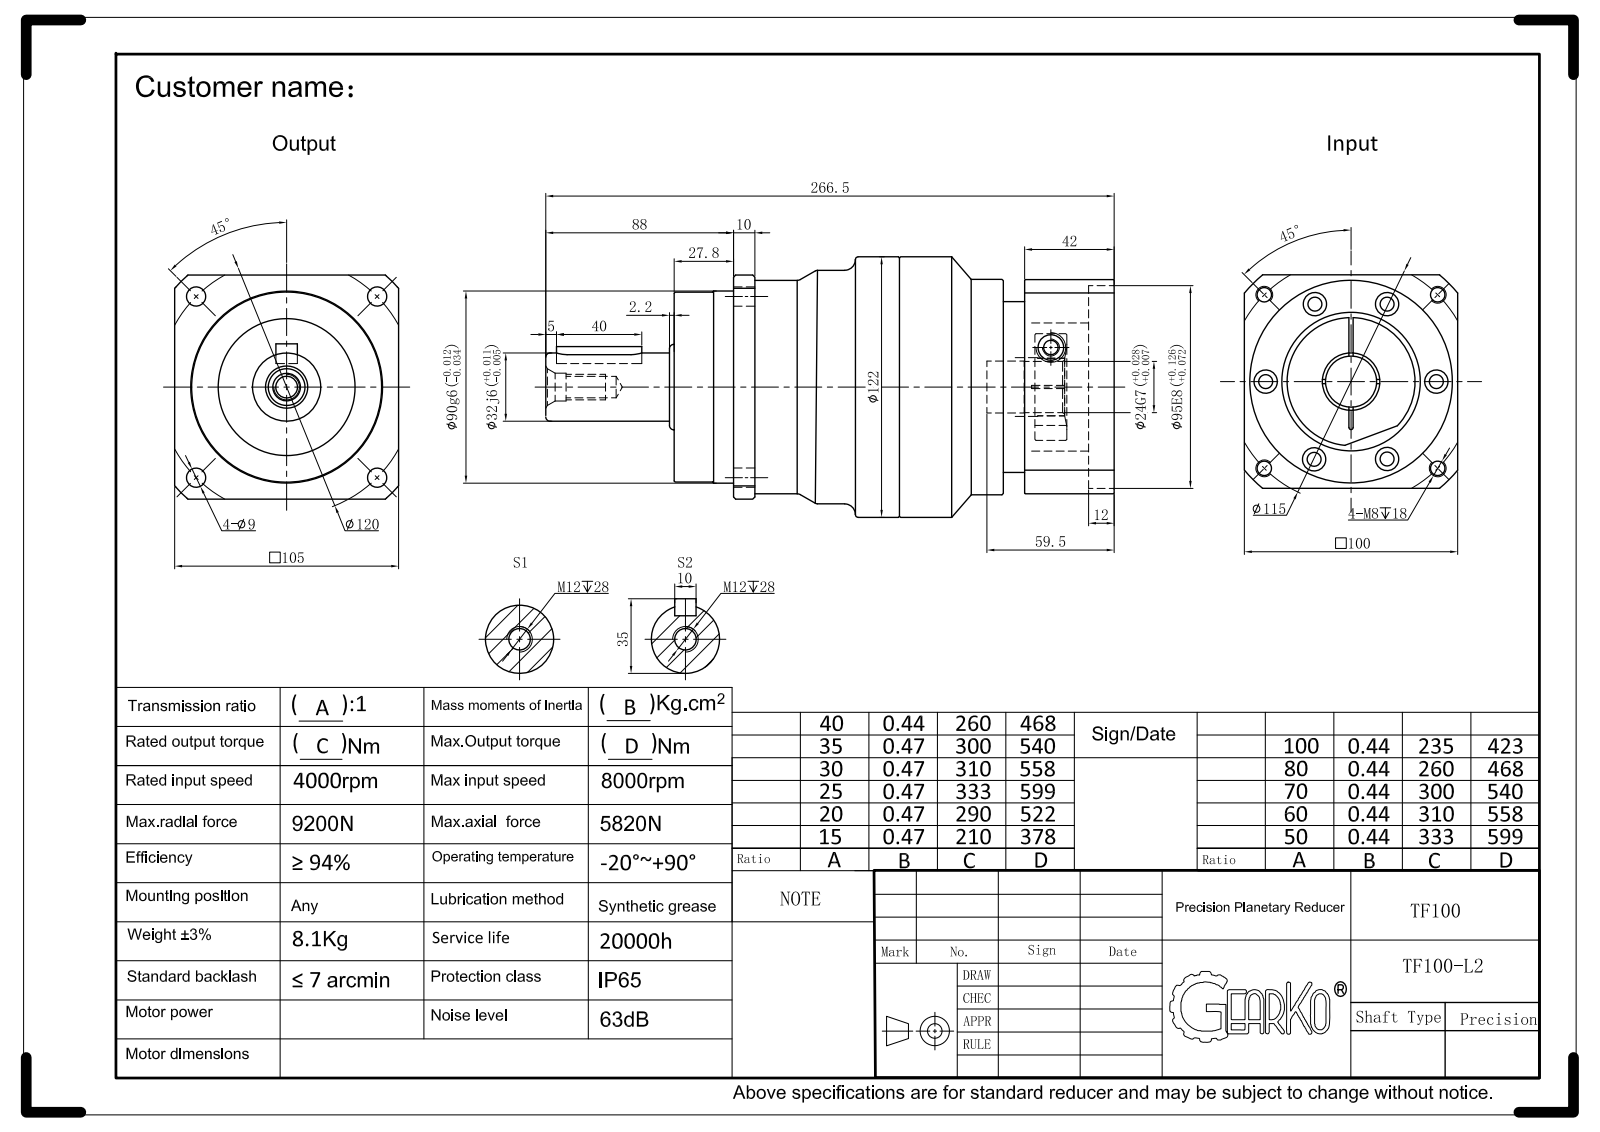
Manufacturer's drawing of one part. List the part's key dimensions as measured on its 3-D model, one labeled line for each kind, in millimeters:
STEP written by: SolidWorks 2017 (CONFIG_CONTROL_DESIGN)
Units: millimetres
Bodies: 1 solid, 183 faces (27 planar, 64 cylindrical, 92 other)
Overall size (bounding box): 266.51 × 122.07 × 122.07
Volume: 1 786 000 mm³ · Surface area: 132 498 mm²
Round holes (diameter × count): ⌀6.8 ×4, ⌀9 ×4, ⌀10.1 ×1, ⌀13 ×1, ⌀24.07 ×1, ⌀24.37 ×1, ⌀27 ×1, ⌀60.07 ×1, ⌀95.07 ×1
Round bosses / shafts (diameter × count): ⌀122.07 ×1, ⌀109.4 ×1, ⌀100.98 ×1, ⌀100 ×1, ⌀90 ×1, ⌀89 ×1, ⌀80.07 ×1, ⌀50 ×1
Partial cylindrical surfaces — rounded edges, fillets, slot ends (radius × count): R5 ×2, R65 ×1, R70 ×1
Main face-to-face distances: 100, 10, 126.49, 164.31, 27.82, 136.49, 194.31, 166.49, 30, 2.5
Hole centre spacings: 2.5, 57.5, 81.32, 83.13, 117.5, 60, 60.01, 83.08
